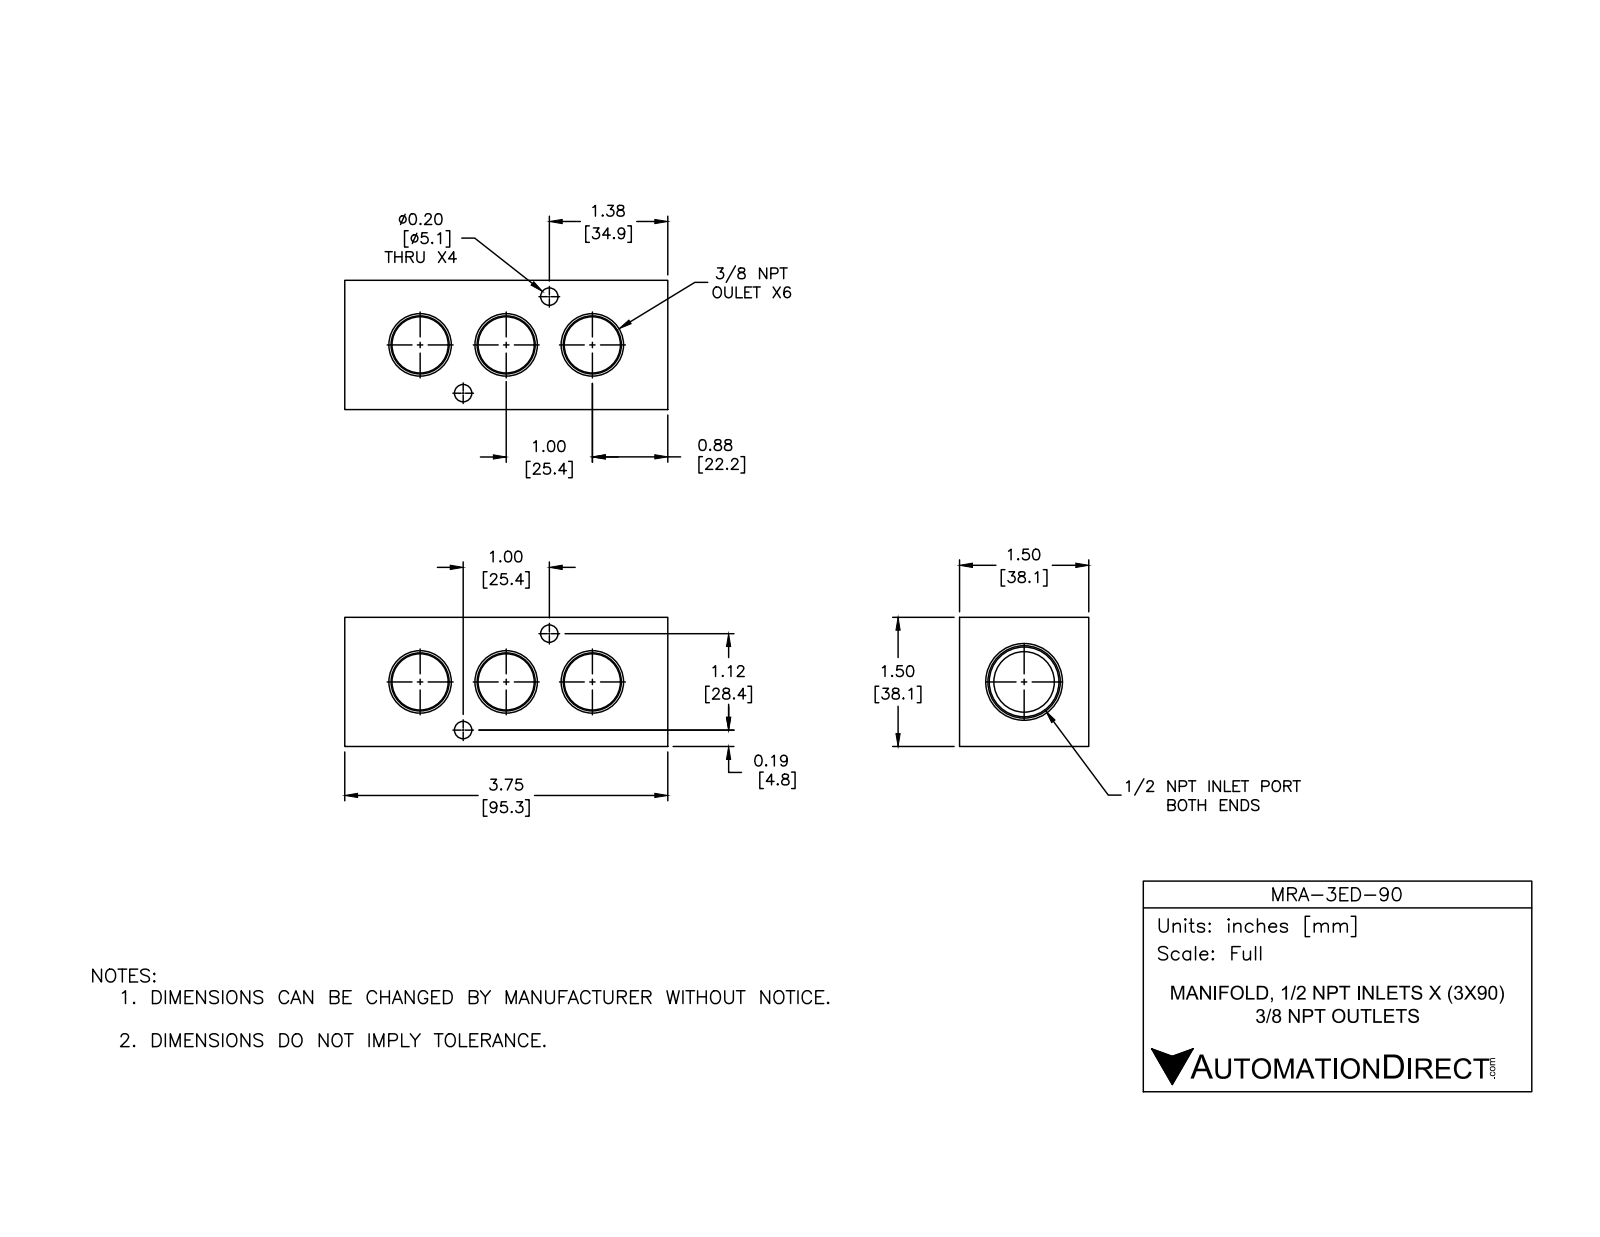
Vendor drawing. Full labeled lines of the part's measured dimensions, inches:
Part name (STEP PRODUCT): MRA-3ED-90
STEP written by: SolidWorks 2015 (CONFIG_CONTROL_DESIGN)
Units: inches
Bodies: 1 solid, 82 faces (20 planar, 30 cylindrical, 32 other)
Overall size (bounding box): 3.75 × 1.5 × 1.5
Volume: 5.762 in³ · Surface area: 39.98 in²
Round holes (diameter × count): ⌀0.562 ×6, ⌀0.2 ×4, ⌀0.703 ×1
Main face-to-face distances: 1.5, 3.75, 1.09, 0.41, 0.53, 3.22, 2.69
Hole centre spacings: 0.751, 1, 1.601, 1.501, 2
